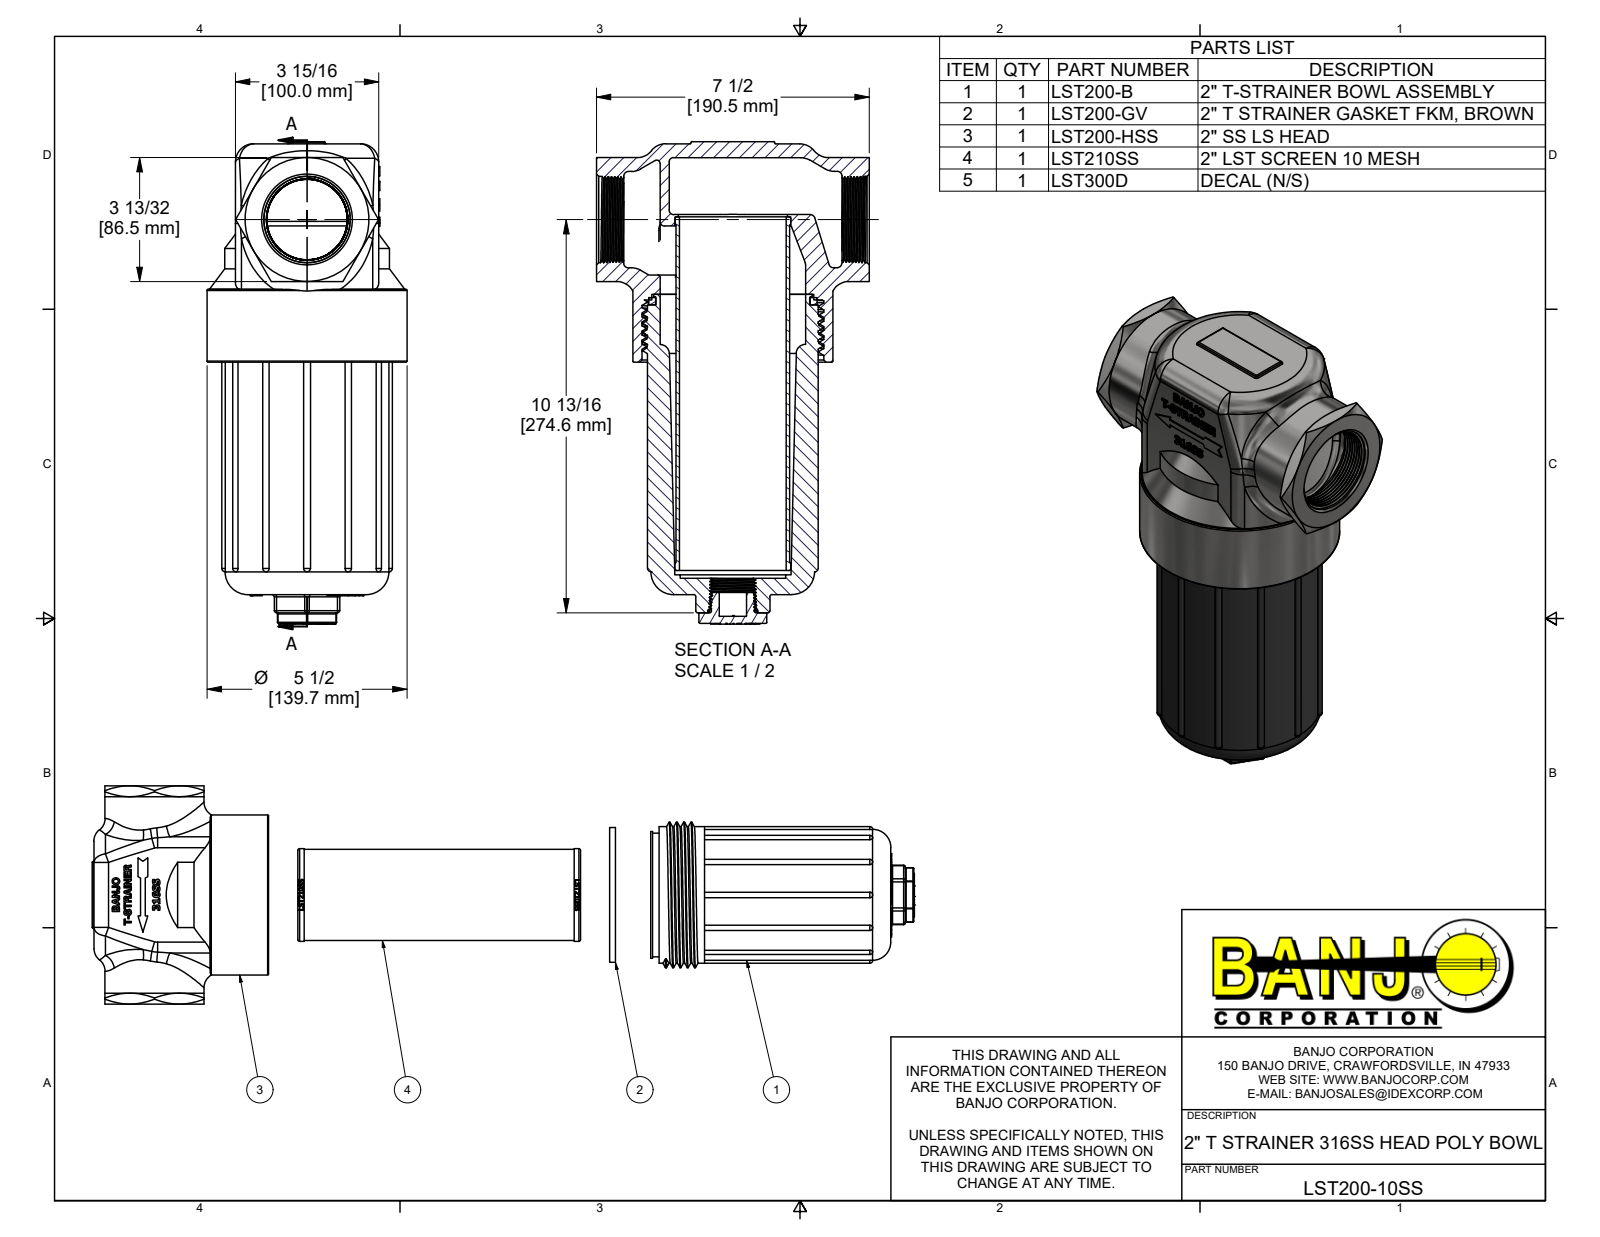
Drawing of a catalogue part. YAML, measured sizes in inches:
part_name: "LST200-10SS; LST200-HSS; LST200B; LST200XB (+4 more)"
step_written_by: "Autodesk Inventor 2019 (AUTOMOTIVE_DESIGN)"
units: inches
bodies: {solids: 6, faces: 1907, planar: 799, cylindrical: 180, other: 928}
overall_size: [21.417, 7.5, 5.5]
volume: 110.3
surface_area: 950.7
round_holes:
  - {diameter: 0.75, count: 1}
  - {diameter: 2.646, count: 1}
  - {diameter: 2.9, count: 1}
  - {diameter: 2.937, count: 1}
  - {diameter: 3, count: 1}
  - {diameter: 3.18, count: 1}
  - {diameter: 3.2, count: 1}
  - {diameter: 4, count: 1}
  - {diameter: 4.225, count: 1}
  - {diameter: 4.458, count: 1}
  - {diameter: 4.729, count: 1}
  - {diameter: 5, count: 1}
round_bosses_or_shafts:
  - {diameter: 5.5, count: 1}
  - {diameter: 4.693, count: 1}
  - {diameter: 4.631, count: 1}
  - {diameter: 4.5, count: 1}
  - {diameter: 4.36, count: 1}
  - {diameter: 4.25, count: 1}
  - {diameter: 3.406, count: 1}
  - {diameter: 3.188, count: 1}
partial_cylinders:
  - {radius: 0.03, count: 28}
  - {radius: 0.094, count: 21}
  - {radius: 0.125, count: 21}
  - {radius: 0.06, count: 12}
  - {radius: 0.5, count: 8}
  - {radius: 0.09, count: 2}
  - {radius: 0.12, count: 2}
  - {radius: 0.391, count: 1}
face_to_face_distances: [0.38, 3.557, 0.38, 3.938, 4.047, 4.427, 7.515, 11.562, 11.942, 0.29]
